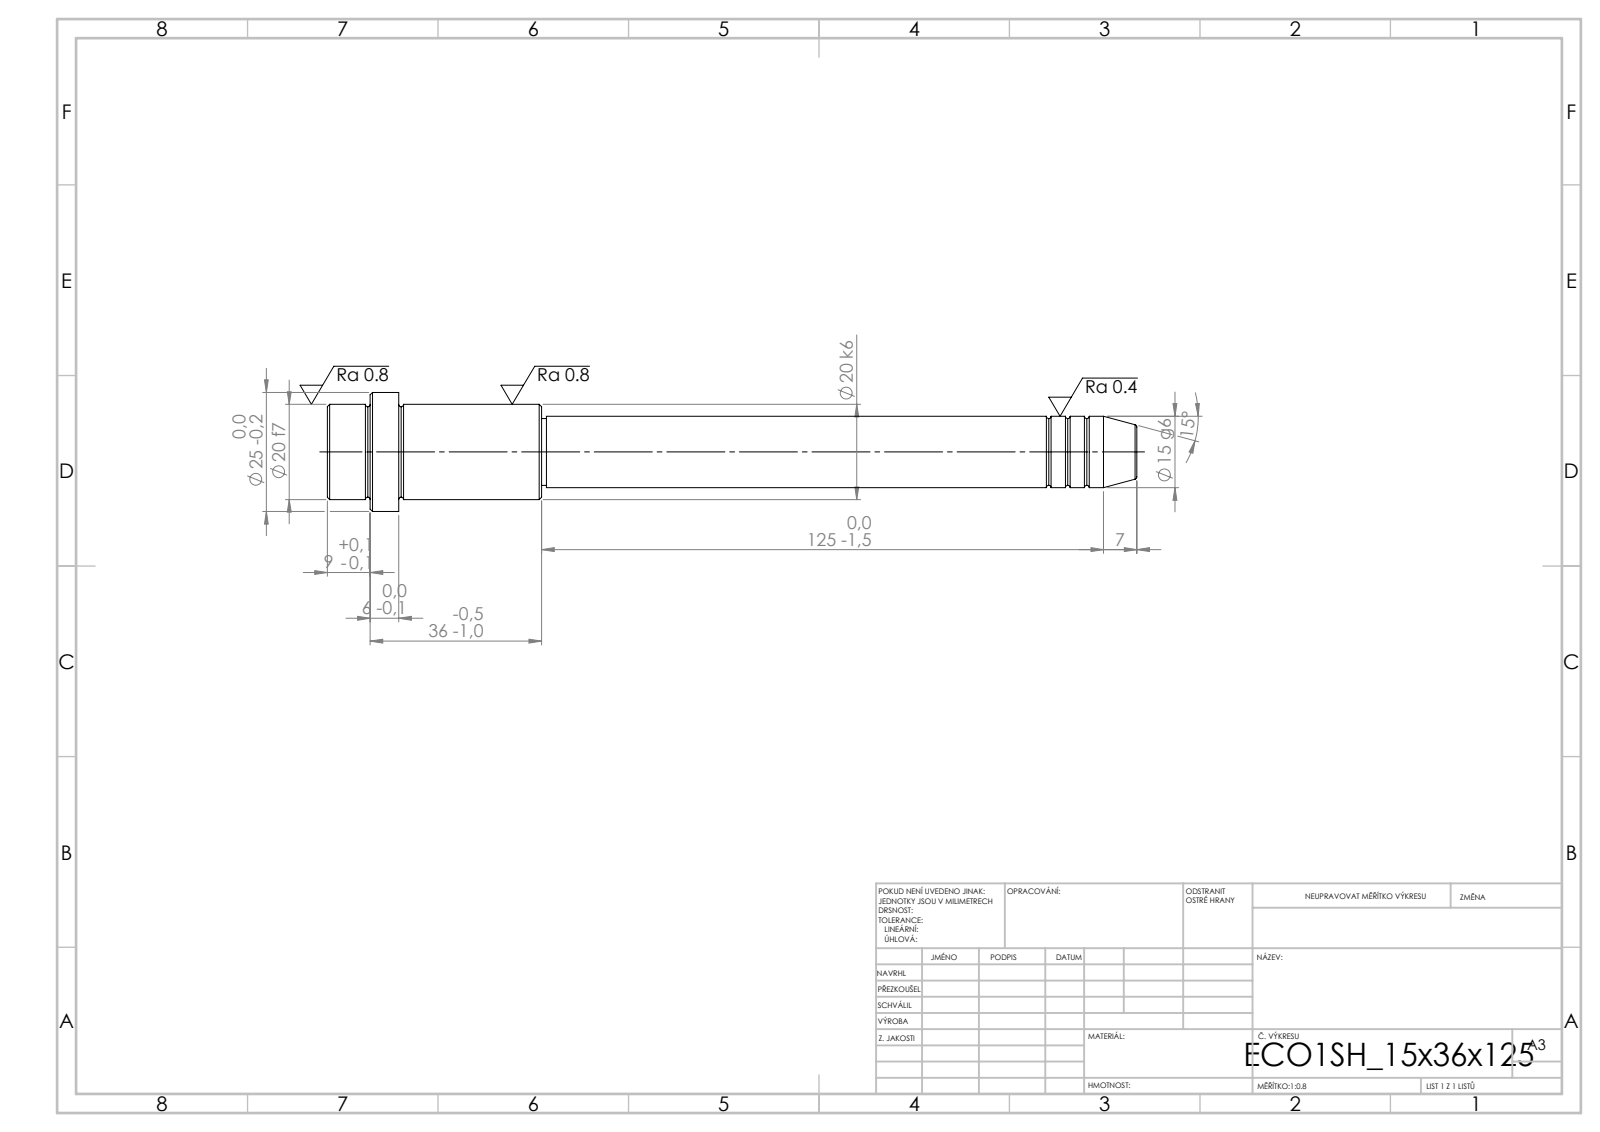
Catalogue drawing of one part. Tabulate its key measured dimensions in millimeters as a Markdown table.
| quantity | value |
| --- | --- |
| STEP written by | SolidWorks 2019 (CONFIG_CONTROL_DESIGN) |
| units | millimeters |
| bodies | 1 solid, 52 faces (6 planar, 16 cylindrical, 30 other) |
| overall size | 170 × 25 × 25 |
| volume | 36 852 mm³ |
| surface area | 9 800 mm² |
| round bosses / shafts (diameter × count) | 25 × 1, 20 × 1, 15 × 1, 14 × 1 |
| main face-to-face distances | 15, 6, 9, 30, 36, 45, 125, 155, 161, 170 |
